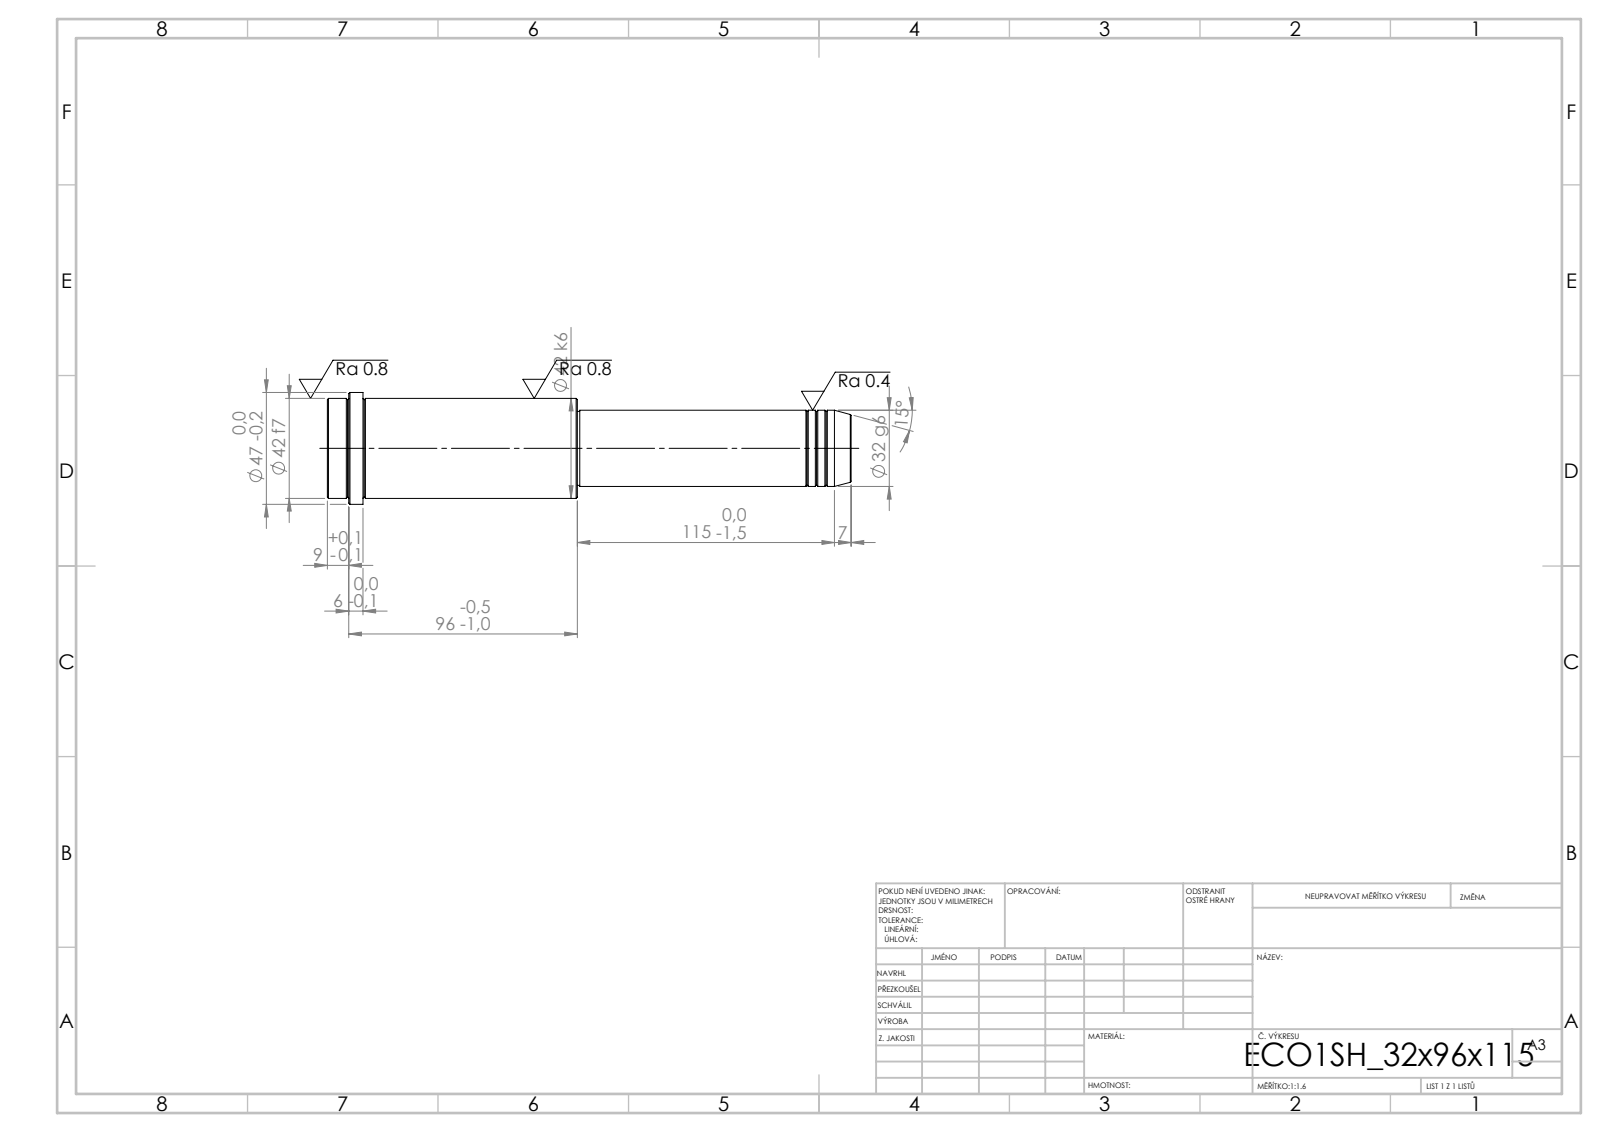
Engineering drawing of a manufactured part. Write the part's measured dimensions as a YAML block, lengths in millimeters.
step_written_by: "SolidWorks 2019 (CONFIG_CONTROL_DESIGN)"
units: millimeters
bodies: {solids: 1, faces: 52, planar: 6, cylindrical: 16, other: 30}
overall_size: [220, 47, 47]
volume: 239100
surface_area: 29056
round_bosses_or_shafts:
  - {diameter: 47, count: 1}
  - {diameter: 42, count: 1}
  - {diameter: 32, count: 1}
  - {diameter: 31, count: 1}
face_to_face_distances: [220, 115, 105, 205, 90, 15, 211, 96, 6, 9]
